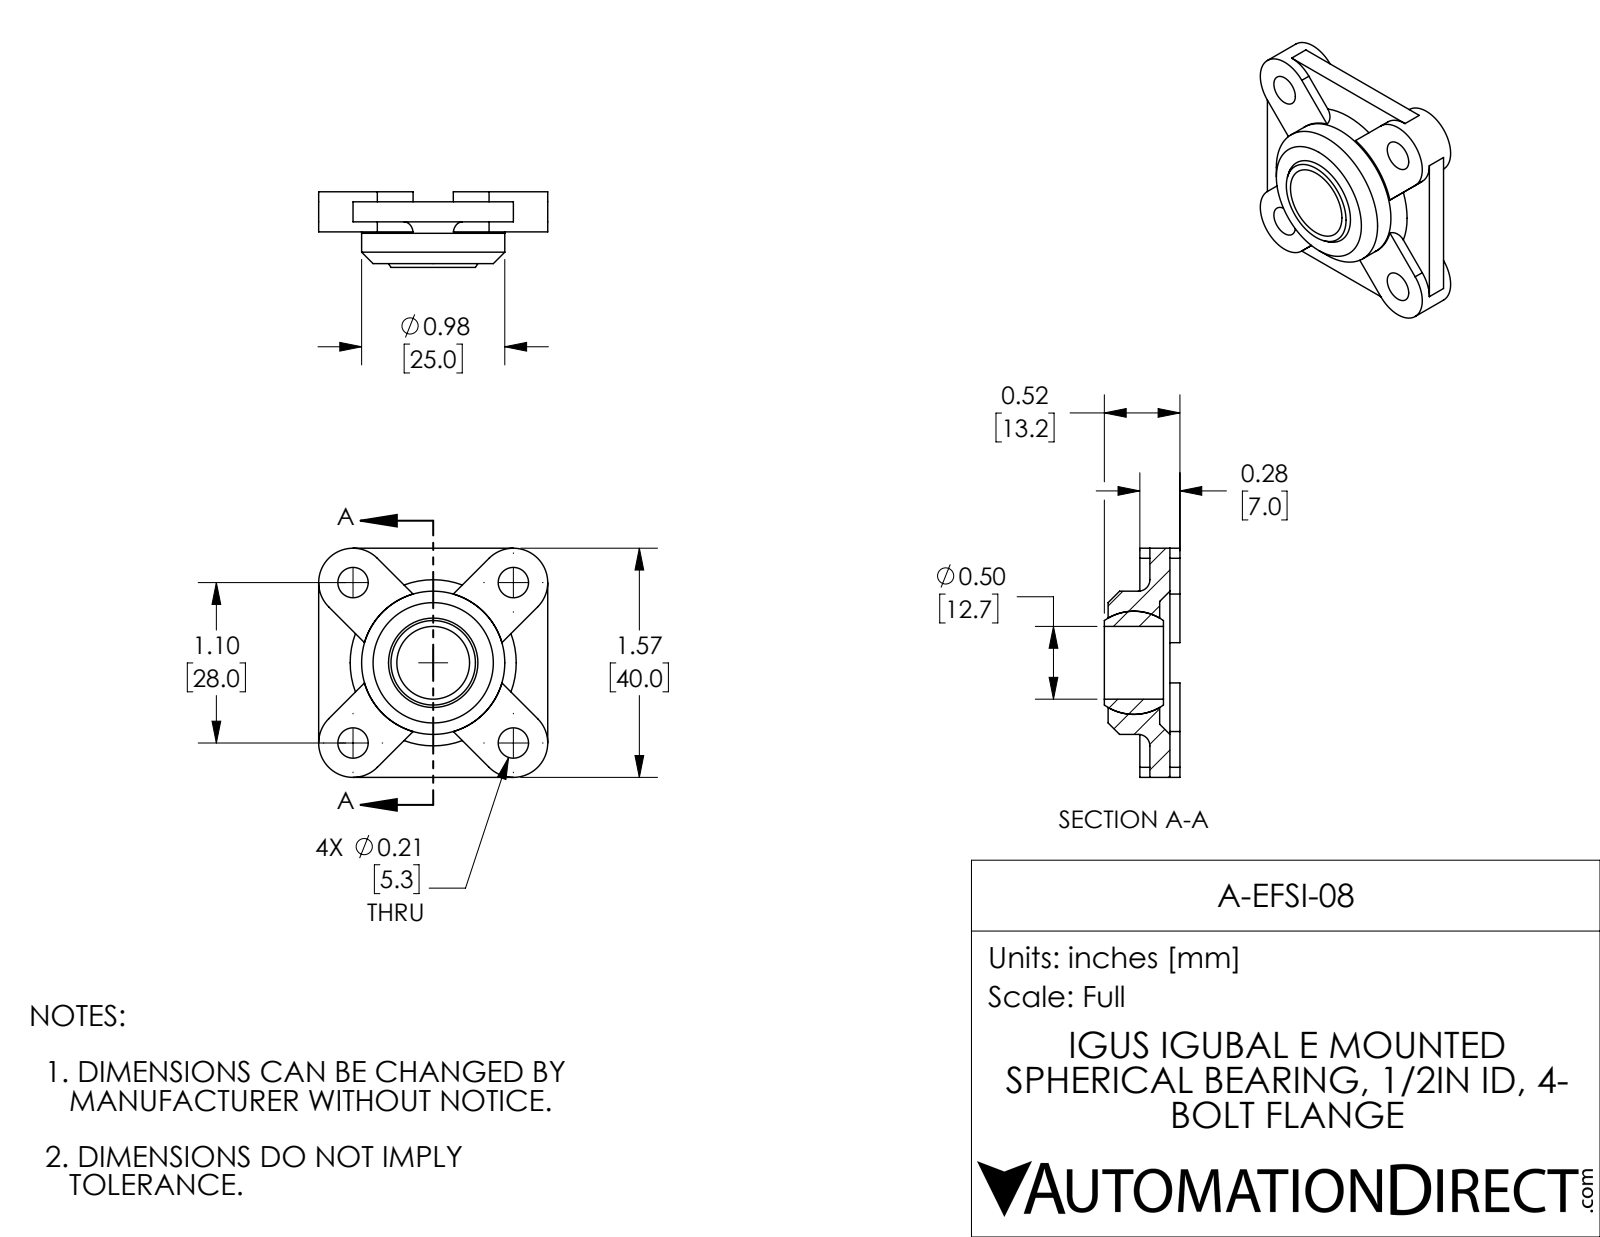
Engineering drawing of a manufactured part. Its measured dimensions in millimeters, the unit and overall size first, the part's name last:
Units: millimetres
Overall size (bounding box): 40 × 40 × 16.7
Round holes (diameter × count): ⌀5.3 ×4, ⌀12.7 ×1, ⌀25 ×1
Partial cylindrical surfaces — rounded edges, fillets, slot ends (radius × count): R6 ×4
Main face-to-face distances: 1.8, 5.3, 7, 3.5, 40, 3.5, 1.8, 1.7, 3.5, 12.5
Hole centre spacings: 19.8, 28, 39.6
Volume: 8 600 mm³ · Surface area: 6 172 mm²
Bodies: 2 solids, 74 faces (40 planar, 24 cylindrical, 10 other)
Part name (STEP PRODUCT): A-EFSI-08
STEP written by: SolidWorks 2017 (AUTOMOTIVE_DESIGN)
